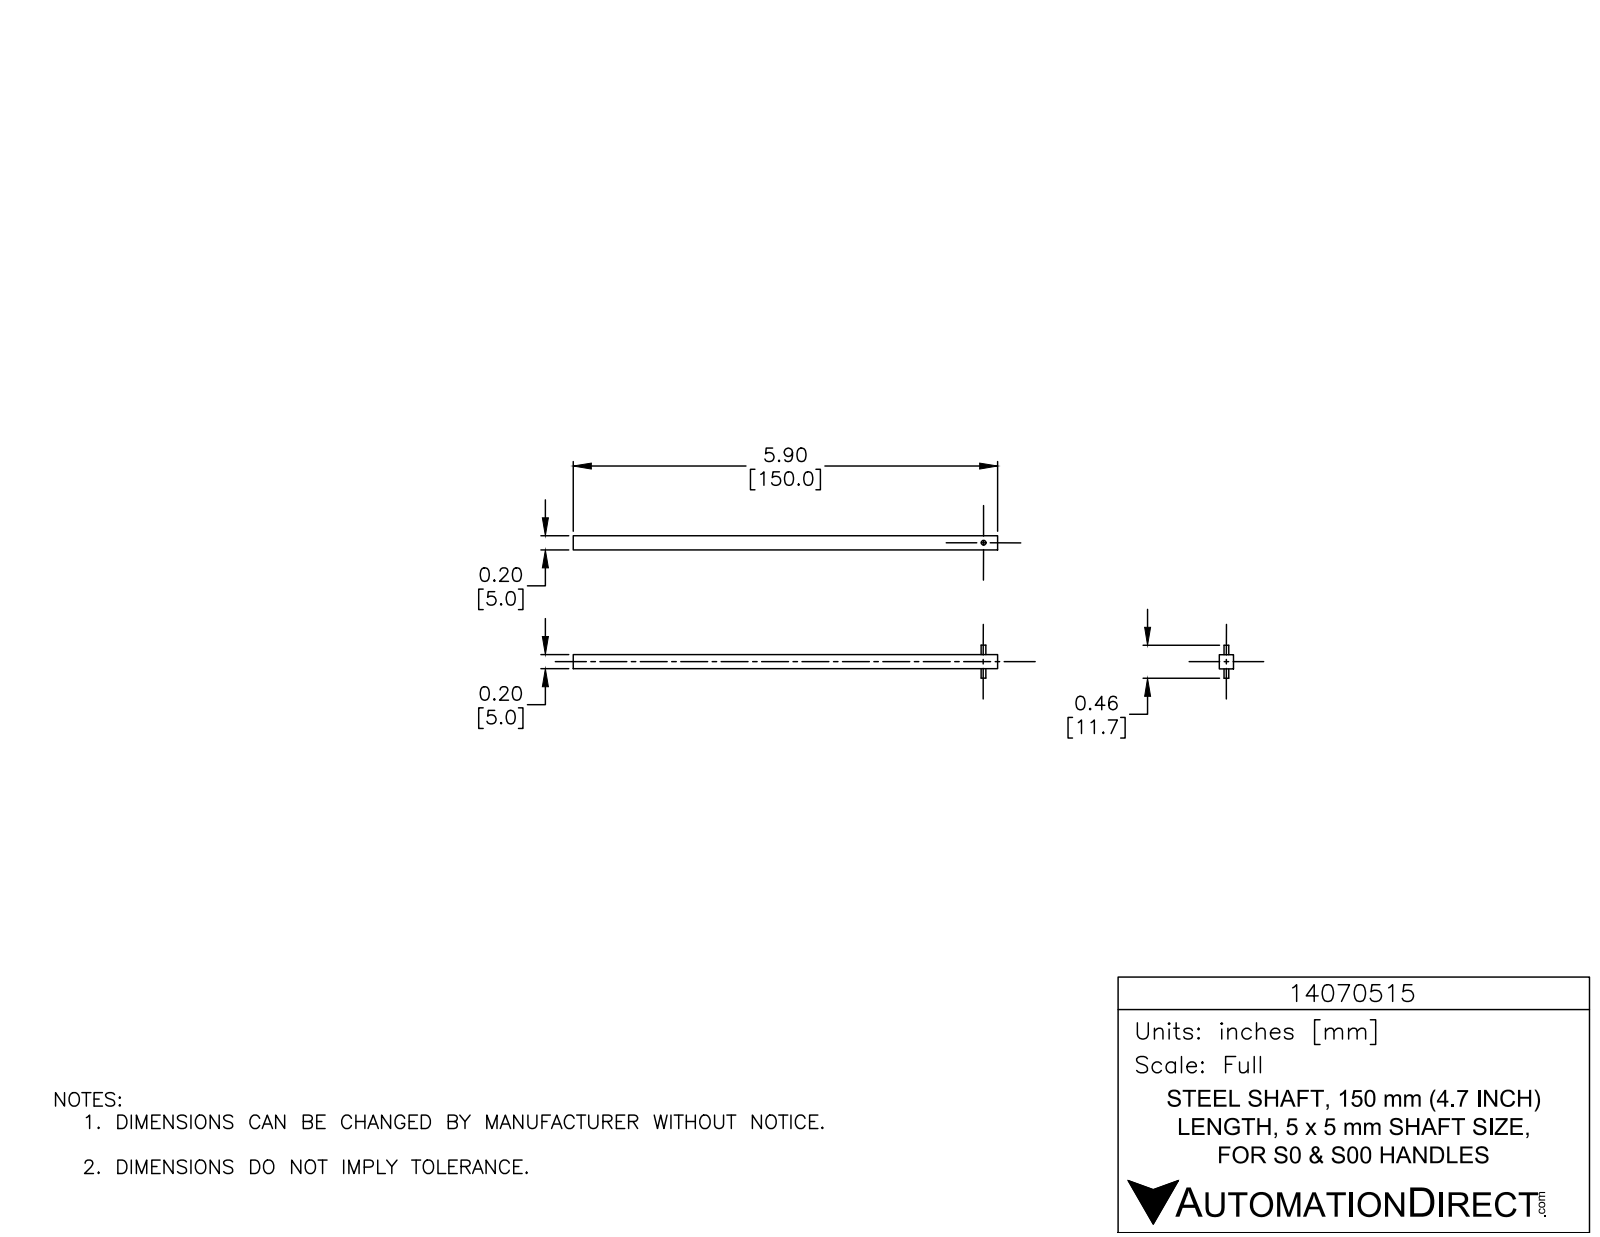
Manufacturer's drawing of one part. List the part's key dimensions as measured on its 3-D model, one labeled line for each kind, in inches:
Part name (STEP PRODUCT): 14070515
STEP written by: SolidWorks 2015 (AUTOMOTIVE_DESIGN)
Units: inches
Bodies: 1 solid, 12 faces (8 planar, 4 cylindrical, 0 other)
Overall size (bounding box): 5.906 × 0.459 × 0.197
Volume: 0.23 in³ · Surface area: 4.782 in²
Round bosses / shafts (diameter × count): ⌀0.066 ×1
Main face-to-face distances: 0.197, 5.906, 0.131, 0.328, 0.459
